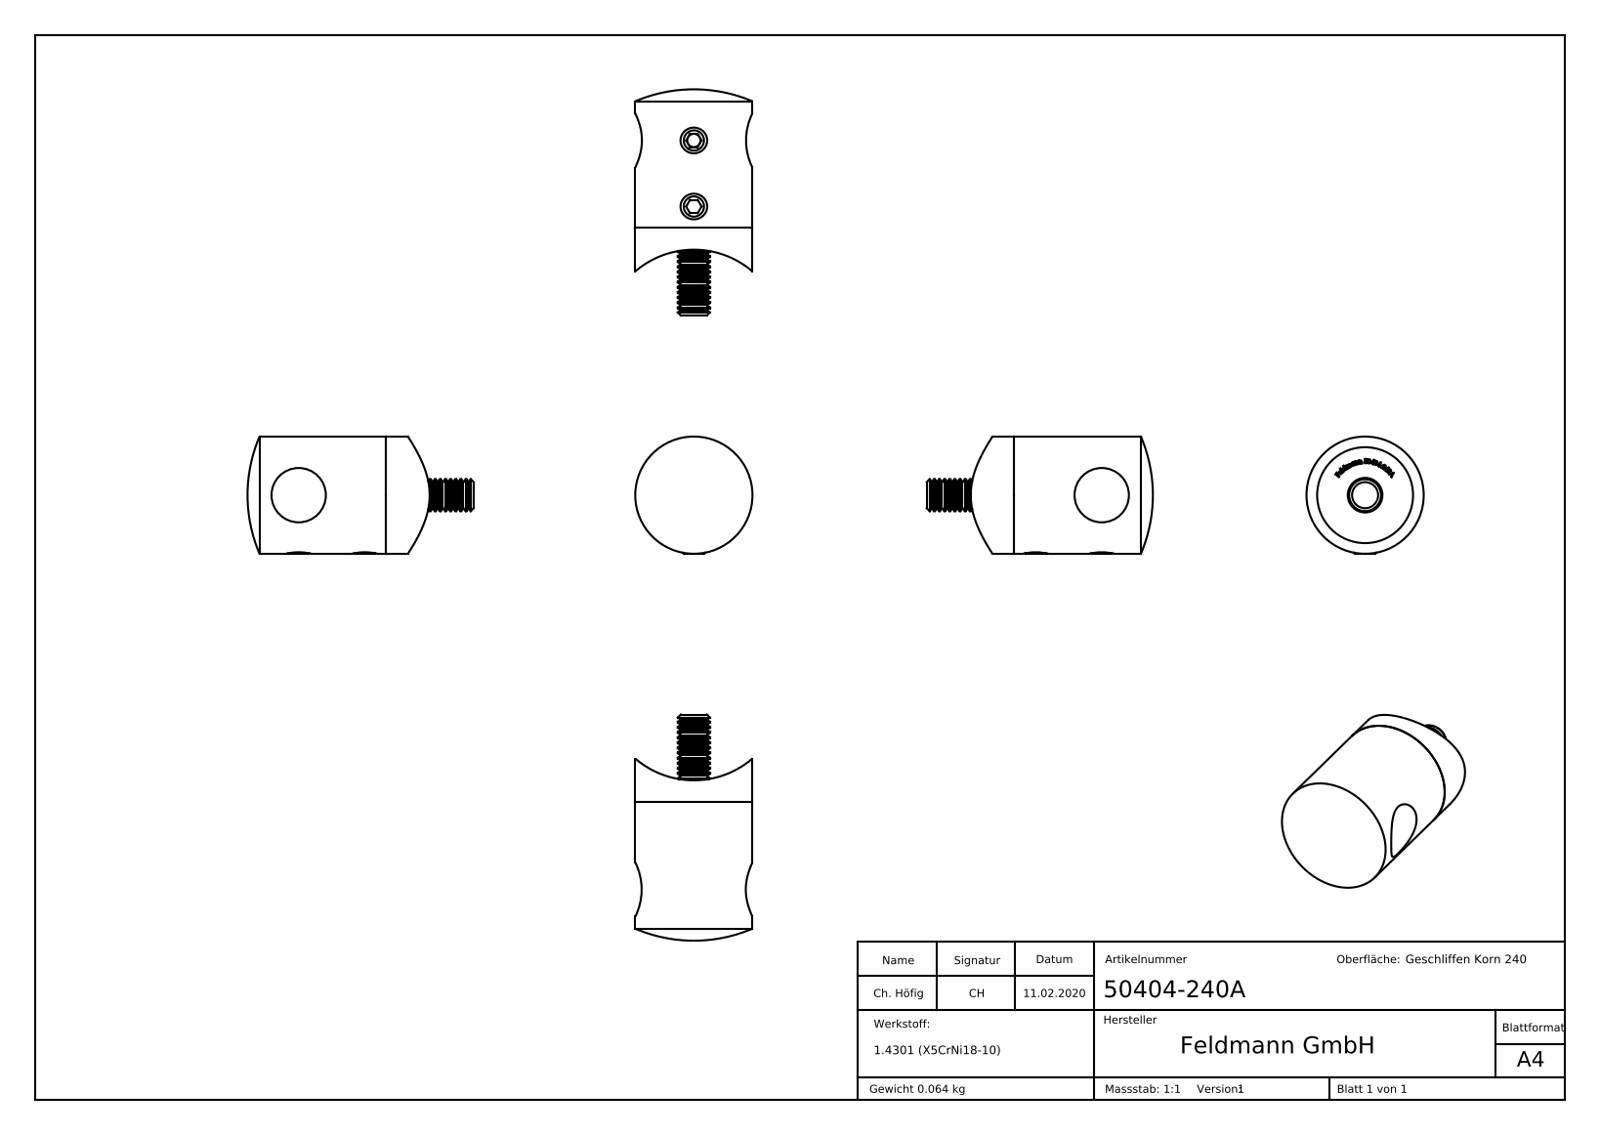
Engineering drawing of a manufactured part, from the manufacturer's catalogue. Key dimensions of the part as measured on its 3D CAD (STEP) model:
Part name (STEP PRODUCT): DIN913_DIN 913 M5x5; 50404-240A; Querstabhalter Teil2 Konfig_50XXX-240A Teil2 33,7; DIN913 (+7 more)
STEP written by: SolidWorks 2015 (CONFIG_CONTROL_DESIGN)
Units: millimetres
Bodies: 5 solids, 375 faces (192 planar, 36 cylindrical, 147 other)
Overall size (bounding box): 70 × 42.45 × 22
Volume: 8 729 mm³ · Surface area: 6 191 mm²
Round holes (diameter × count): ⌀4.2 ×2, ⌀6.5 ×1, ⌀10.2 ×1, ⌀12 ×1, ⌀18 ×1
Round bosses / shafts (diameter × count): ⌀5 ×2, ⌀22 ×1, ⌀11.9 ×1, ⌀11.57 ×1, ⌀6 ×1
Partial cylindrical surfaces — rounded edges, fillets, slot ends (radius × count): R16.85 ×1
Main face-to-face distances: 2.1, 10.65, 8.55, 2.5, 9.6, 7.5, 1.05, 14.35, 16.45, 23.95
Hole centre spacings: 12.4
